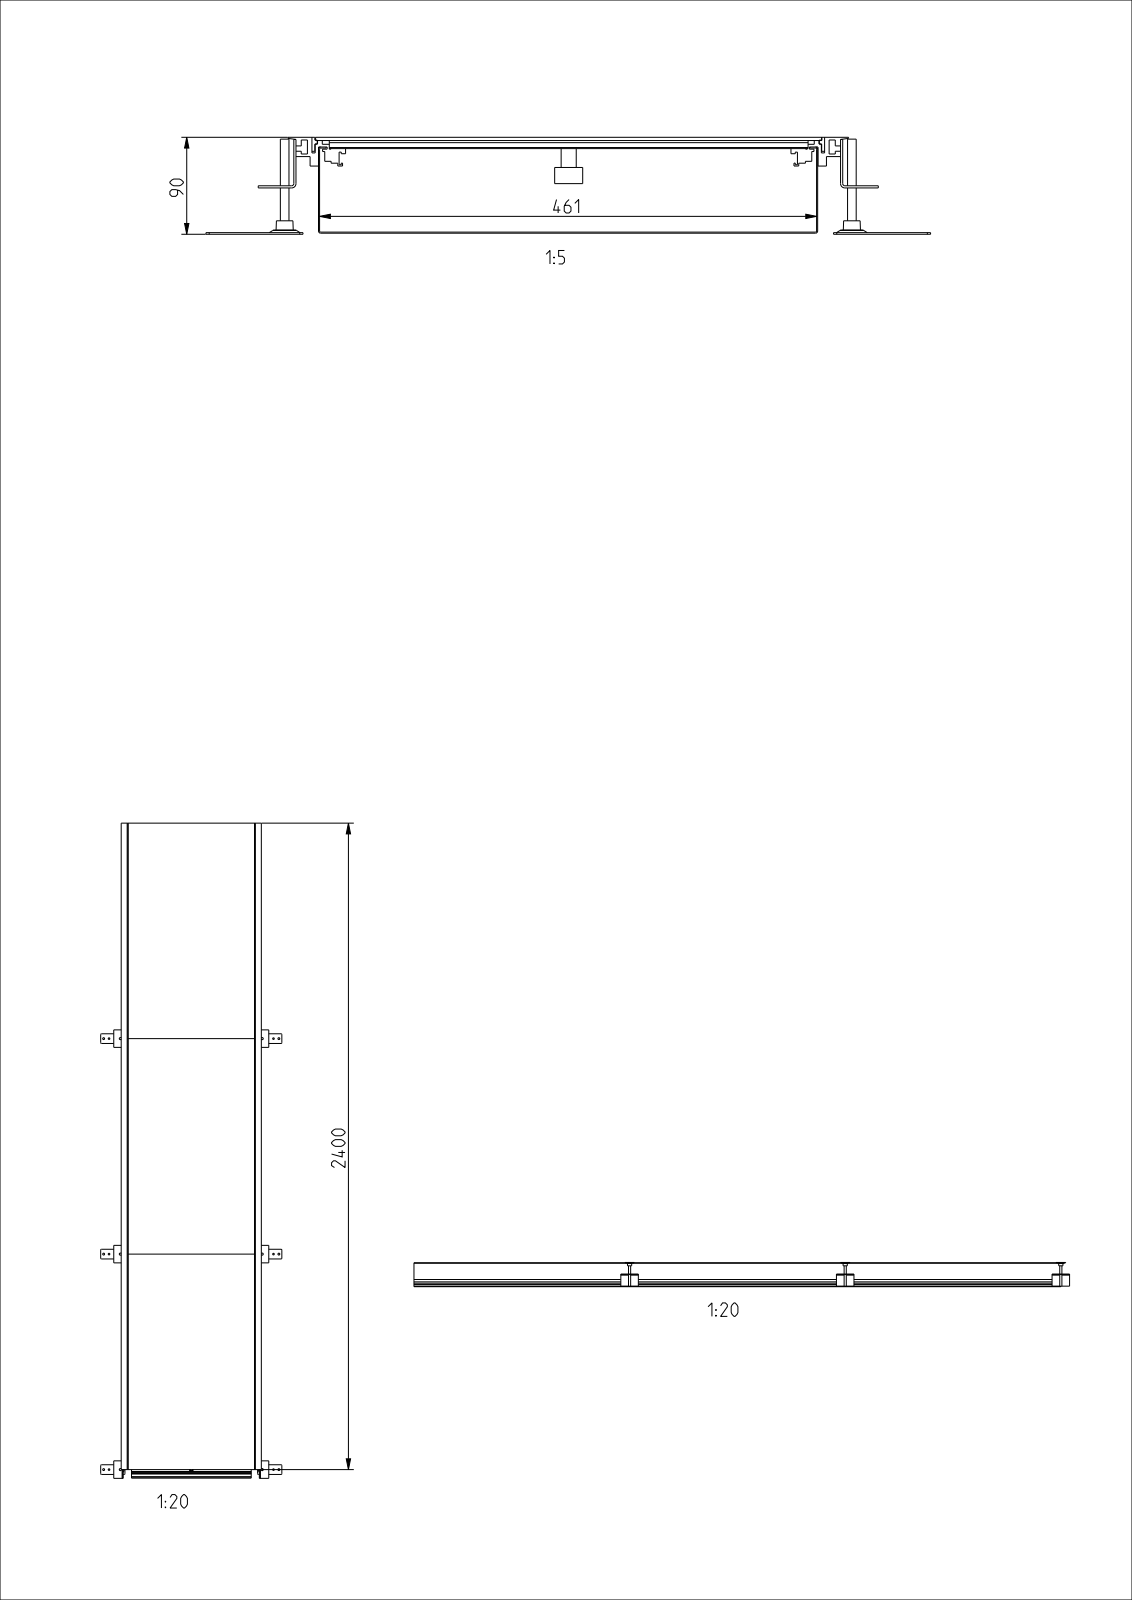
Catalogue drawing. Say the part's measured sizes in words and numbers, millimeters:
The part is named "U05644KUN; U05650KUN; U05647KUN; U05826KUN (+8 more)". Its 3-D file was written by "CREO PARAMETRIC BY PTC INC, 2020281 (AUTOMOTIVE_DESIGN)". It is 61 solids with 1036 faces: 606 planar, 358 cylindrical and 72 other. Overall it measures 2432.5 by 672.13 by 90 millimeters. Its volume is 9 187 000 cubic millimeters and its surface area 7 684 000 square millimeters. Round holes: 15 of diameter 7, 9 of diameter 8, 9 of diameter 10, 6 of diameter 6, 6 of diameter 8.5, 6 of diameter 11.5, 6 of diameter 17.5, 6 of diameter 23. Round bosses or shafts: 9 of diameter 26, 9 of diameter 14, 9 of diameter 11.9, 6 of diameter 20, 6 of diameter 8. Partial cylindrical surfaces (rounded edges, fillets, slot ends): 96 of radius 2, 24 of radius 3, 20 of radius 0.5, 4 of radius 1, 2 of radius 4. The main face-to-face distances are 1, 3, 86, 89, 85, 88, 462, 7.5, 6.5, 78.5. The hole center spacings are 800, 1600, 800.25, 801.1, 802.4, 981.21, 992.92, 1018.36.
